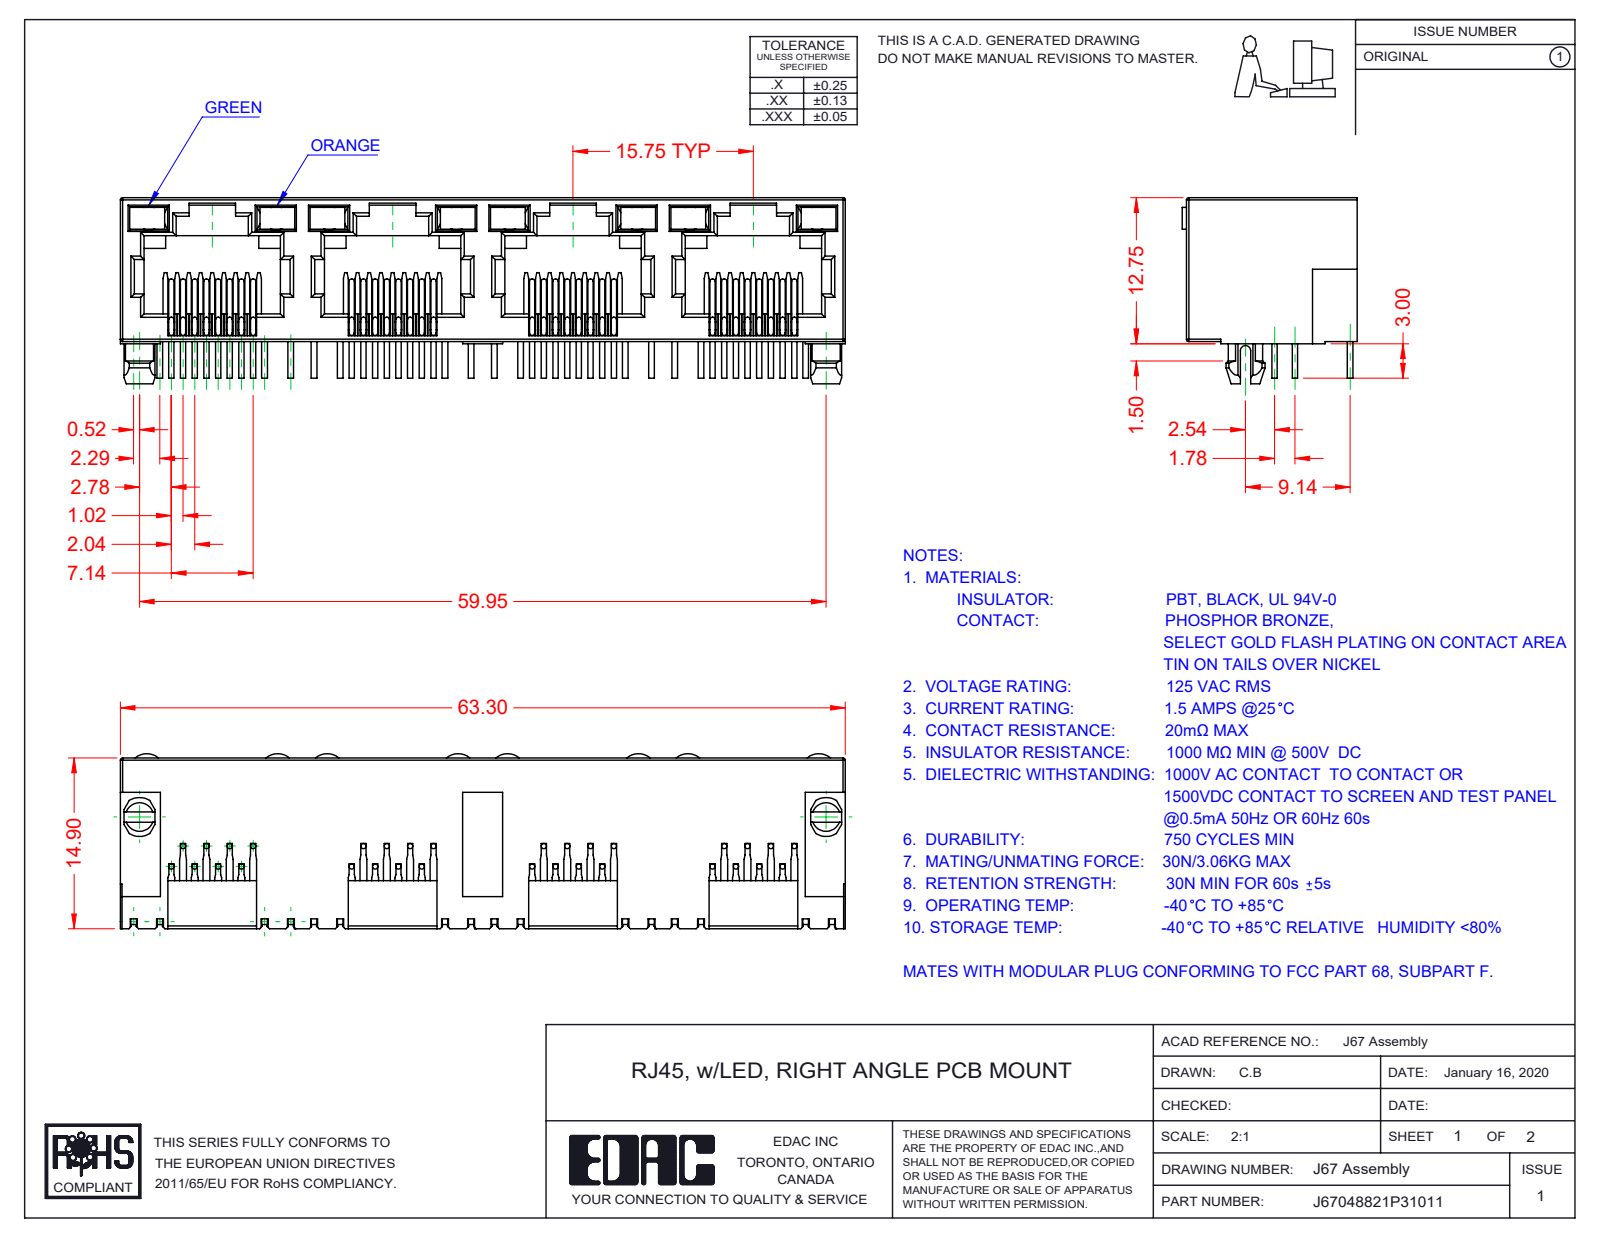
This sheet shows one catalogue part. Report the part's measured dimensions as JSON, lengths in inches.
{"part_name": "67 LED RH_4-Orange; 67 Insulator; J67048822P34011; 67 Contacts (+1 more)", "step_written_by": "SolidWorks 2016 (CONFIG_CONTROL_DESIGN)", "units": "inches", "bodies": {"solids": 41, "faces": 2465, "planar": 1781, "cylindrical": 476, "other": 208}, "overall_size": [2.492, 0.64, 0.602], "volume_in3": 0.315, "surface_area_in2": 17.94, "round_bosses_or_shafts": [[0.018, 96]], "partial_cylinders_radius": [[0.008, 66], [0.012, 29], [0.018, 9], [0.061, 8], [0.059, 2], [0.067, 2], [0.014, 1], [0.039, 1]], "face_to_face_distances": [0.02, 0.494, 0.074, 0.035, 0.394, 0.62, 0.039, 0.055, 0.433, 0.468]}
